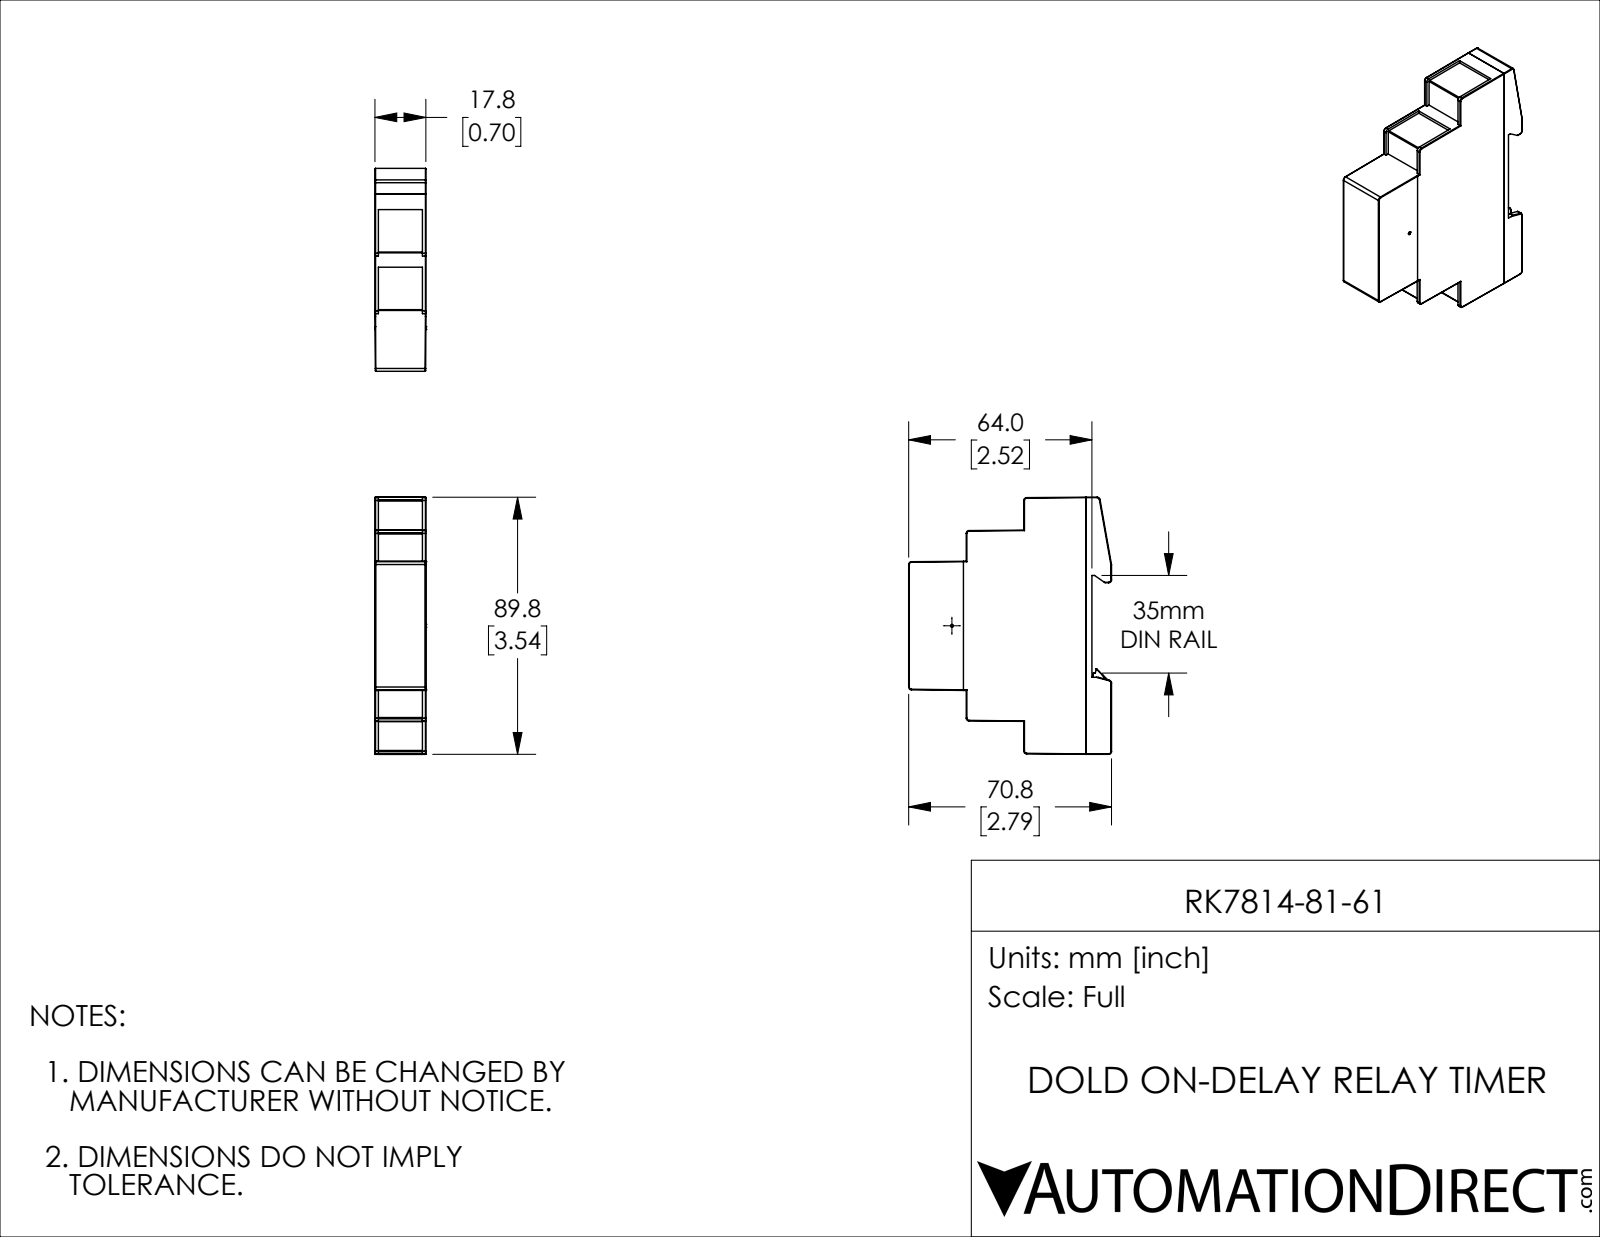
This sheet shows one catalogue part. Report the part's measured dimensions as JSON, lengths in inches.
{"part_name": "RK7814-81-61", "step_written_by": "SolidWorks 2019 (CONFIG_CONTROL_DESIGN)", "units": "inches", "bodies": {"solids": 3, "faces": 267, "planar": 158, "cylindrical": 85, "other": 24}, "overall_size": [3.535, 2.787, 0.701], "volume_in3": 4.945, "surface_area_in2": 31.16, "round_bosses_or_shafts": [[0.039, 1]], "partial_cylinders_radius": [[0.008, 36], [0.039, 12], [0.004, 9], [0.012, 4], [0.02, 2], [0.011, 1], [0.031, 1], [0.118, 1]], "face_to_face_distances": [0.701, 0.085, 2.52, 2.435, 0.383, 0.446, 0.829, 0.791, 0.835, 0.894]}
